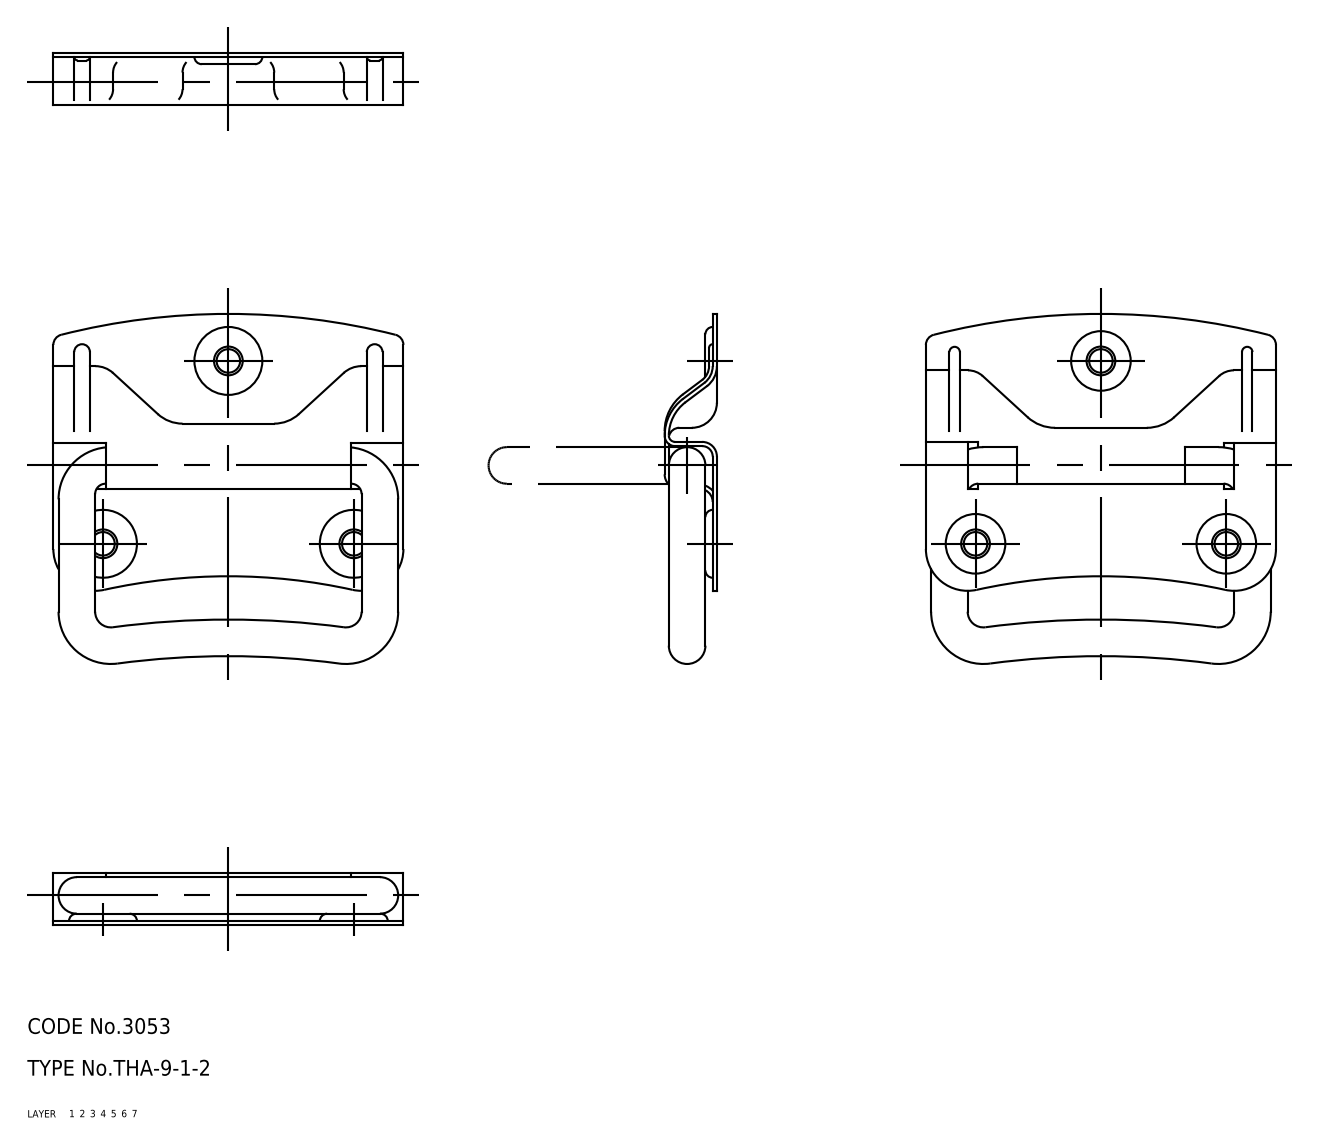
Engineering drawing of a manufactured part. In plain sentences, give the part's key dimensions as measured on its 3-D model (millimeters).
The part is named "grip; base; THA_9_1_2_23737_36". Its 3-D file was written by "CADfix (AUTOMOTIVE_DESIGN)". It is 2 solids with 259 faces: 0 planar, 0 cylindrical and 259 other. Overall it measures 67 by 67 by 10 millimeters. Its volume is 8 848 cubic millimeters and its surface area 11 846 square millimeters.
